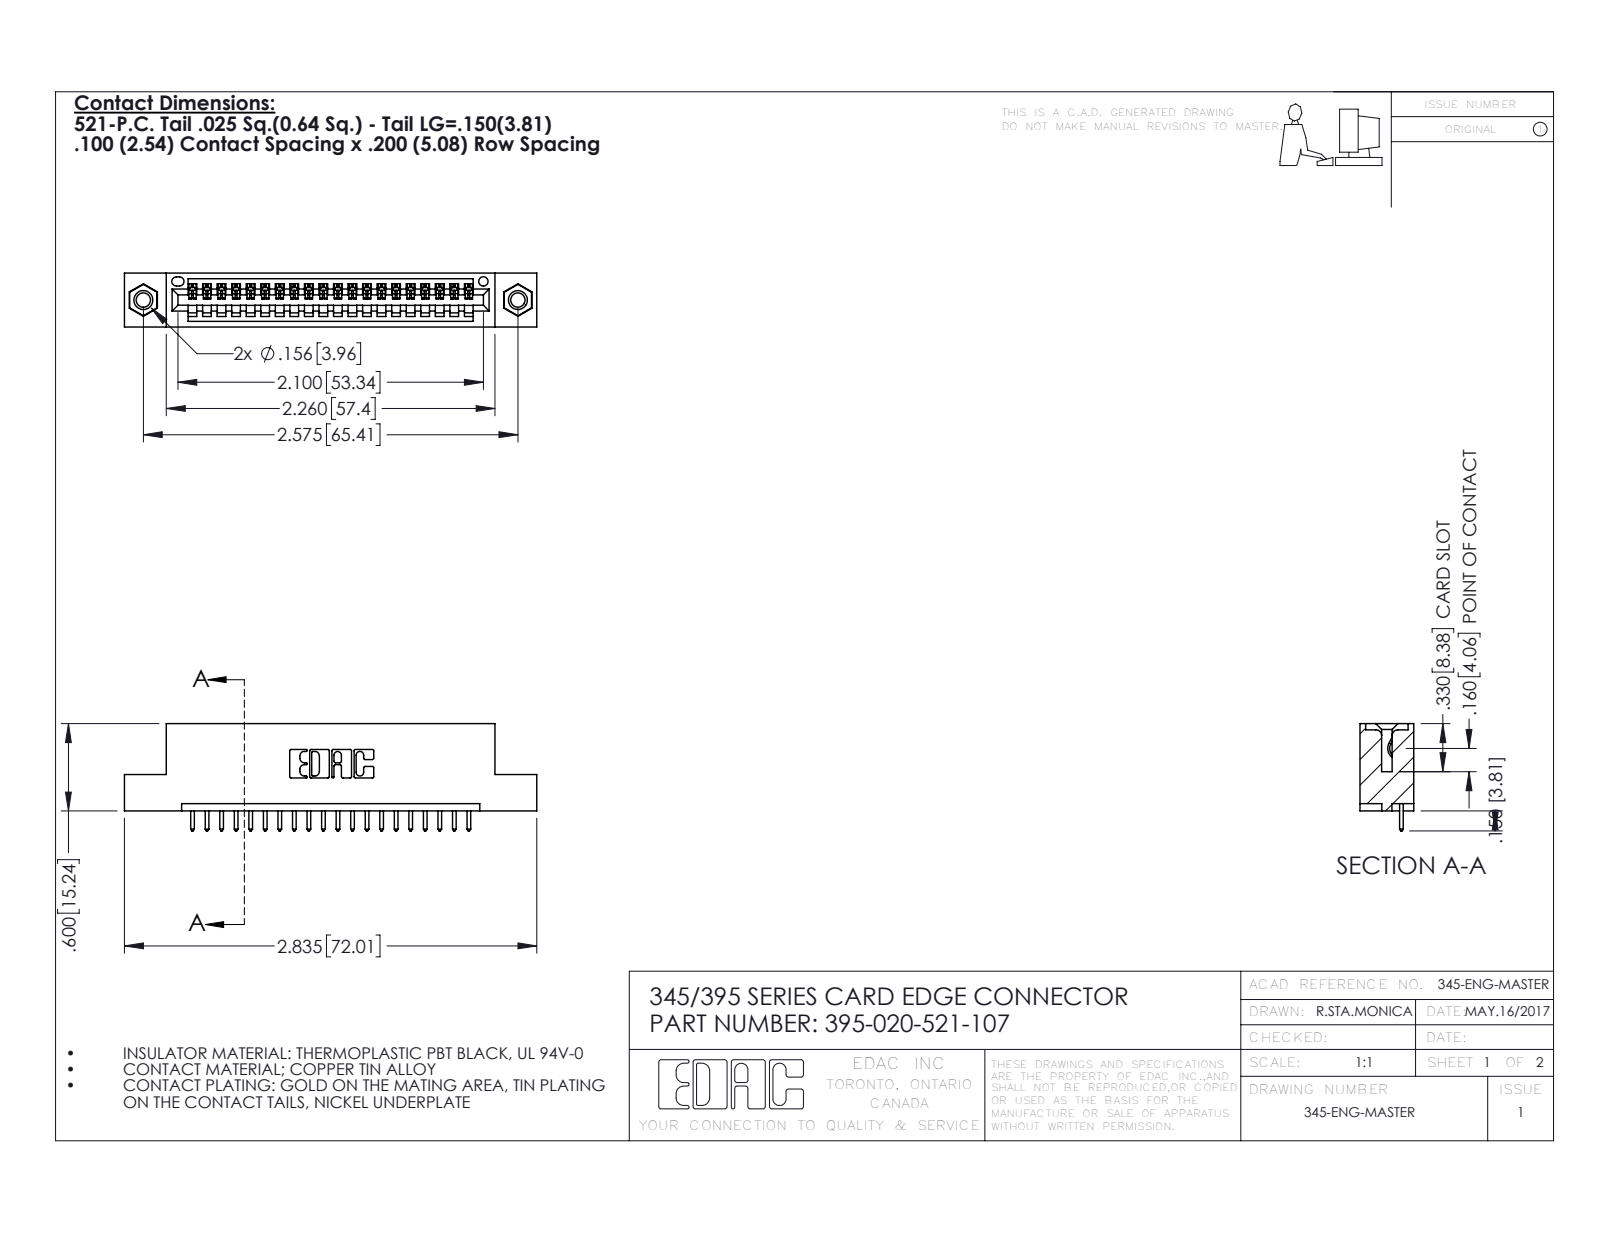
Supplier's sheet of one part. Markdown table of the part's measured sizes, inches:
| quantity | value |
| --- | --- |
| part name | 395-020-521-107; 345 Part_Flush Mounting Lugs - 0.156 Dia-TI; 345-250-001_345-250-005-103; 345-292-001_345-293-121 |
| STEP written by | SolidWorks 2016 (CONFIG_CONTROL_DESIGN) |
| units | inches |
| bodies | 23 solids, 1346 faces (912 planar, 418 cylindrical, 16 other) |
| overall size | 2.835 × 0.737 × 0.37 |
| volume | 0.402 in³ |
| surface area | 12.81 in² |
| round holes (diameter × count) | 0.098 × 2, 0.125 × 2, 0.156 × 2, 0.064 × 1 |
| round bosses / shafts (diameter × count) | 0.155 × 2 |
| partial cylindrical surfaces (radius × count) | 0.006 × 40, 0.01 × 40, 0.01 × 22, 0.007 × 6, 0.031 × 6, 0.026 × 3, 0.031 × 2, 0.04 × 2 |
| main face-to-face distances | 0.072, 0.298, 0.2, 0.37, 0.098, 0.272, 0.025, 0.225, 0.149, 0.6 |
| hole center spacings | 0.27, 2.341, 2.575 |
